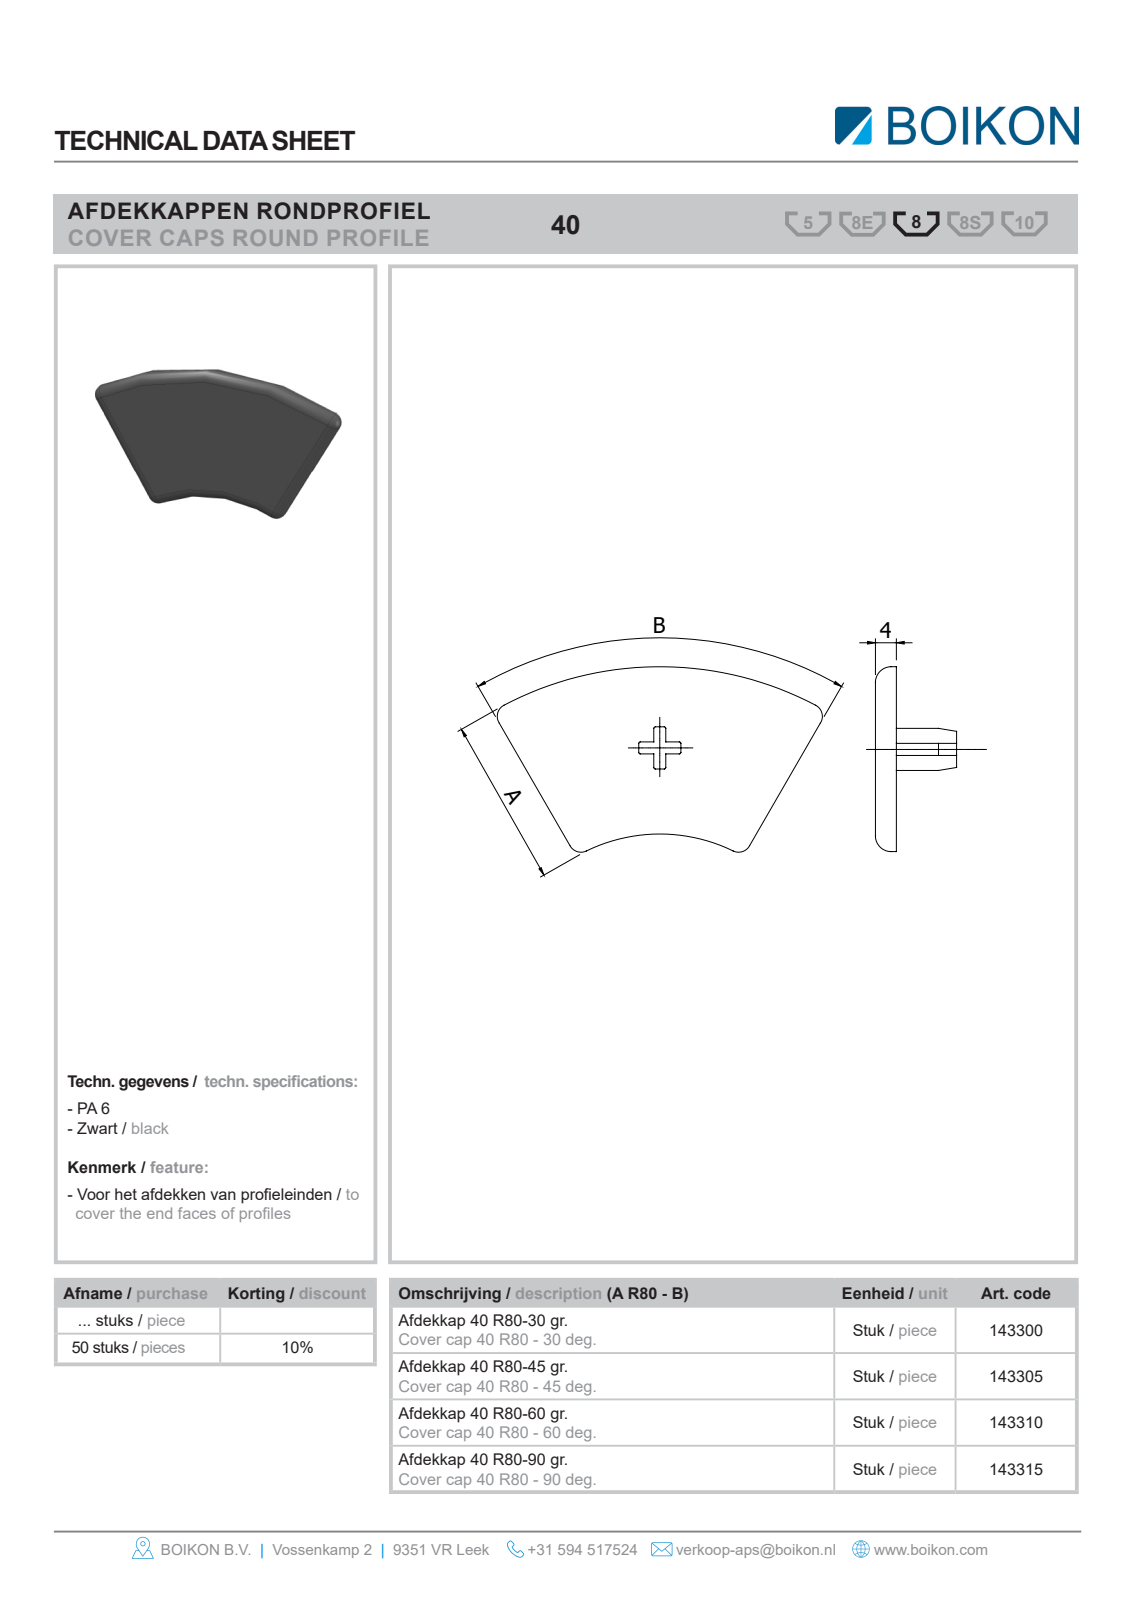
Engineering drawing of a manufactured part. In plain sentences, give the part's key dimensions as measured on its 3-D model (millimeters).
The part is named "Root; 143315Afdekkap 40-90grBOIKON0". Its 3-D file was written by "HiCAD 2013 1802.4 Build 509 (AUTOMOTIVE_DESIGN)". It is 1 solid with 18 faces: 4 planar, 8 cylindrical and 6 other. Overall it measures 79.94 by 79.94 by 4 millimeters. Its volume is 14 549 cubic millimeters and its surface area 8 235 square millimeters. Partial cylindrical surfaces (rounded edges, fillets, slot ends): 6 of radius 3, 1 of radius 40, 1 of radius 80. The main face-to-face distances are 4.
